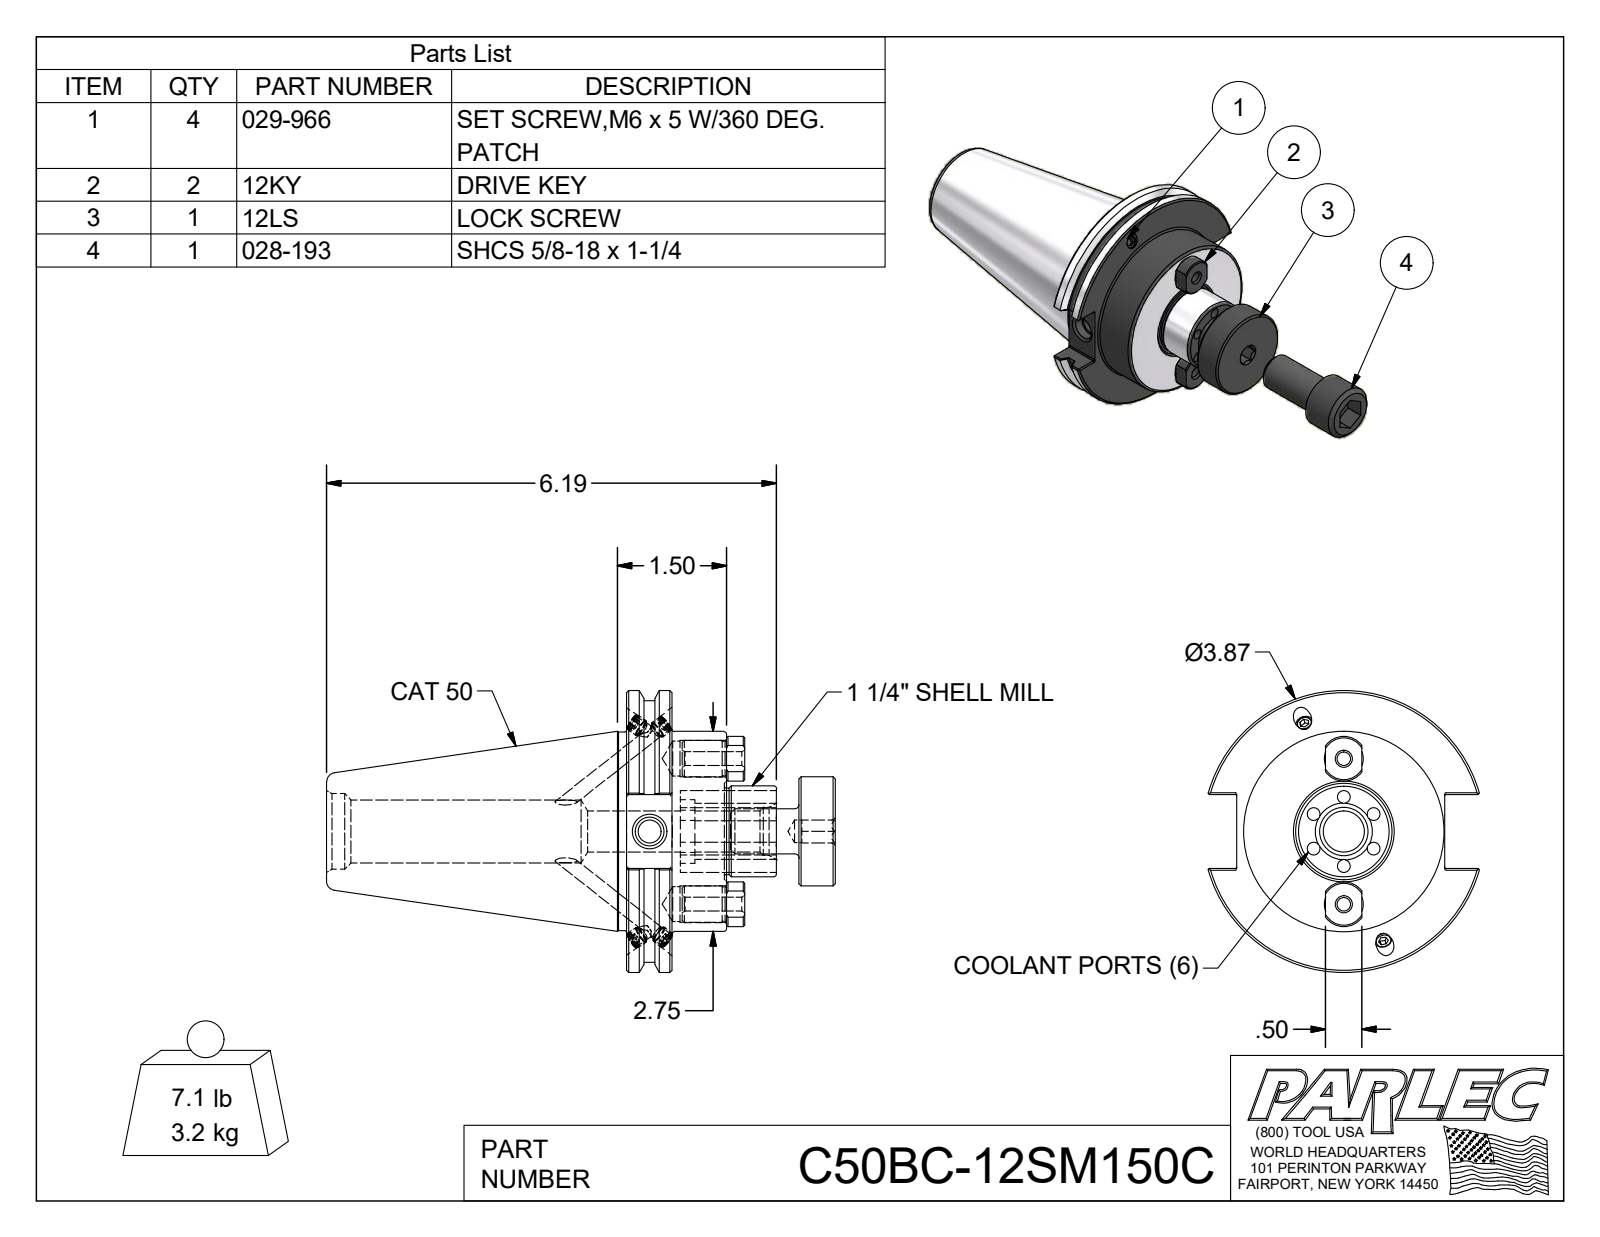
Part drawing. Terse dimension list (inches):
name: C50BC-12SM150C-1; 028-193; 12KY; 12LS (+5 more)
written by: Autodesk Inventor 2016 (AUTOMOTIVE_DESIGN)
unit: in
bodies: 9 solids, 268 faces (113 planar, 80 cylindrical, 75 other)
size: 9.487 × 3.875 × 3.729
volume: 26.15 in³; area: 108.5 in²
holes: 6× ⌀0.177, 4× ⌀0.197, 4× ⌀0.24, 2× ⌀0.19, 2× ⌀0.48, 2× ⌀0.5, 1× ⌀0.312, 1× ⌀0.315, 1× ⌀0.399, 1× ⌀0.565, 1× ⌀0.66, 1× ⌀0.865
bosses: 4× ⌀0.244, 4× ⌀0.236, 2× ⌀0.505, 2× ⌀0.47, 1× ⌀3.875, 1× ⌀3.594, 1× ⌀2.75, 1× ⌀2.73
rounds: 12× R0.02, 2× R0.307, 1× R0.446
face distances: 0.625, 1.375, 0.75, 2.872, 2.247, 1.497, 0.5, 2.372, 1.747, 0.997
hole spacings: 0.474, 0.475, 0.822, 0.866, 1.304, 0.526, 0.949, 1
